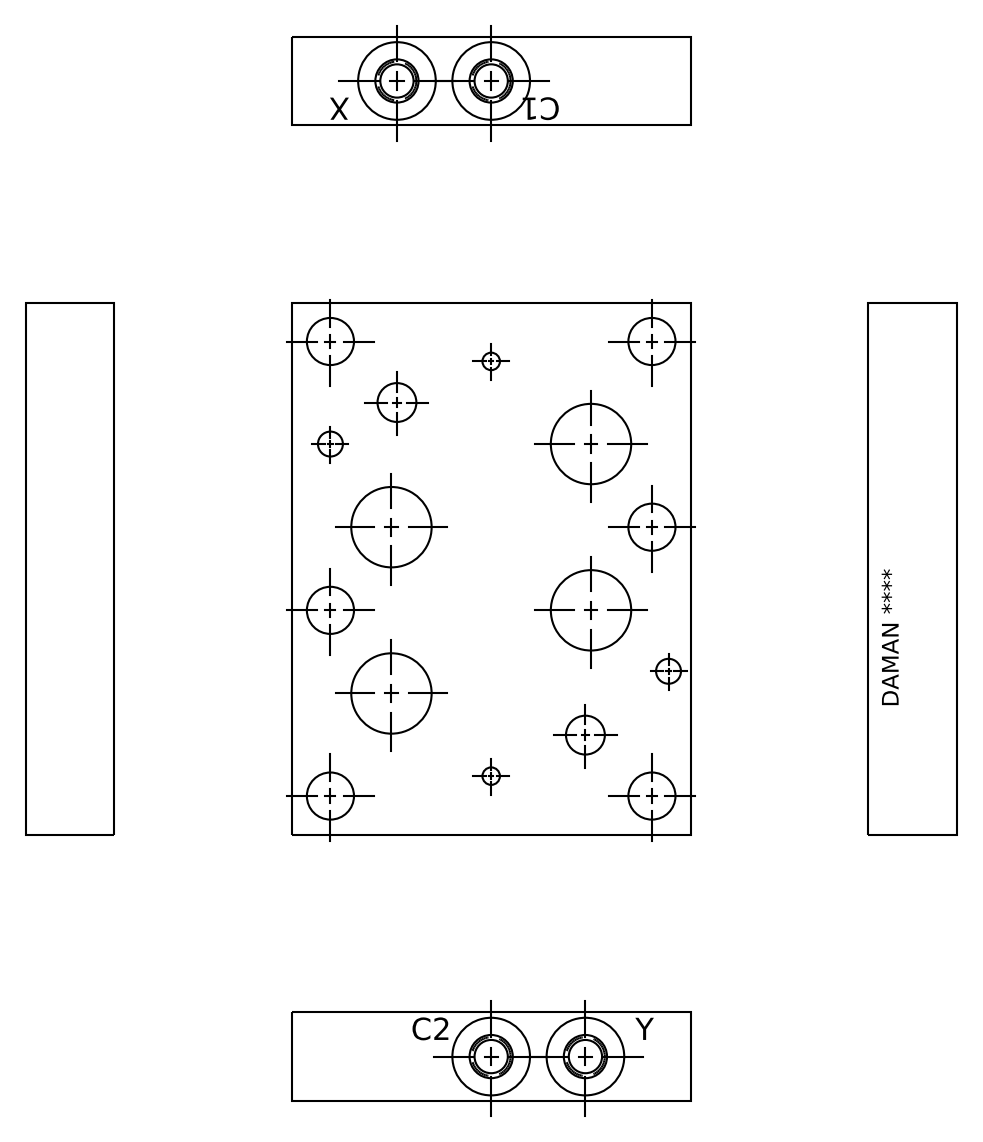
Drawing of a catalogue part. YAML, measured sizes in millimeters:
part_name: "Part_AD08TPXY4S_3D"
step_written_by: "Autodesk Inventor 2019 (AUTOMOTIVE_DESIGN)"
units: millimeters
bodies: {solids: 1, faces: 511, planar: 301, cylindrical: 51, other: 159}
overall_size: [152.4, 114.3, 25.4]
volume: 373324
surface_area: 62907
round_holes:
  - {diameter: 13.51, count: 10}
  - {diameter: 23.01, count: 4}
  - {diameter: 33.35, count: 4}
  - {diameter: 9.53, count: 3}
  - {diameter: 9.88, count: 3}
  - {diameter: 11.13, count: 3}
  - {diameter: 21.29, count: 3}
  - {diameter: 5, count: 2}
  - {diameter: 6.35, count: 2}
  - {diameter: 7.14, count: 2}
  - {diameter: 10.72, count: 2}
  - {diameter: 23.02, count: 2}
face_to_face_distances: [25.4, 114.3, 2.79, 22.61, 152.4, 0.79, 151.61, 150.82, 1, 113.3]
hole_center_spacings: [46.36, 75.08, 92.07, 132.85, 134.3, 25.84, 29.54, 53.18]
